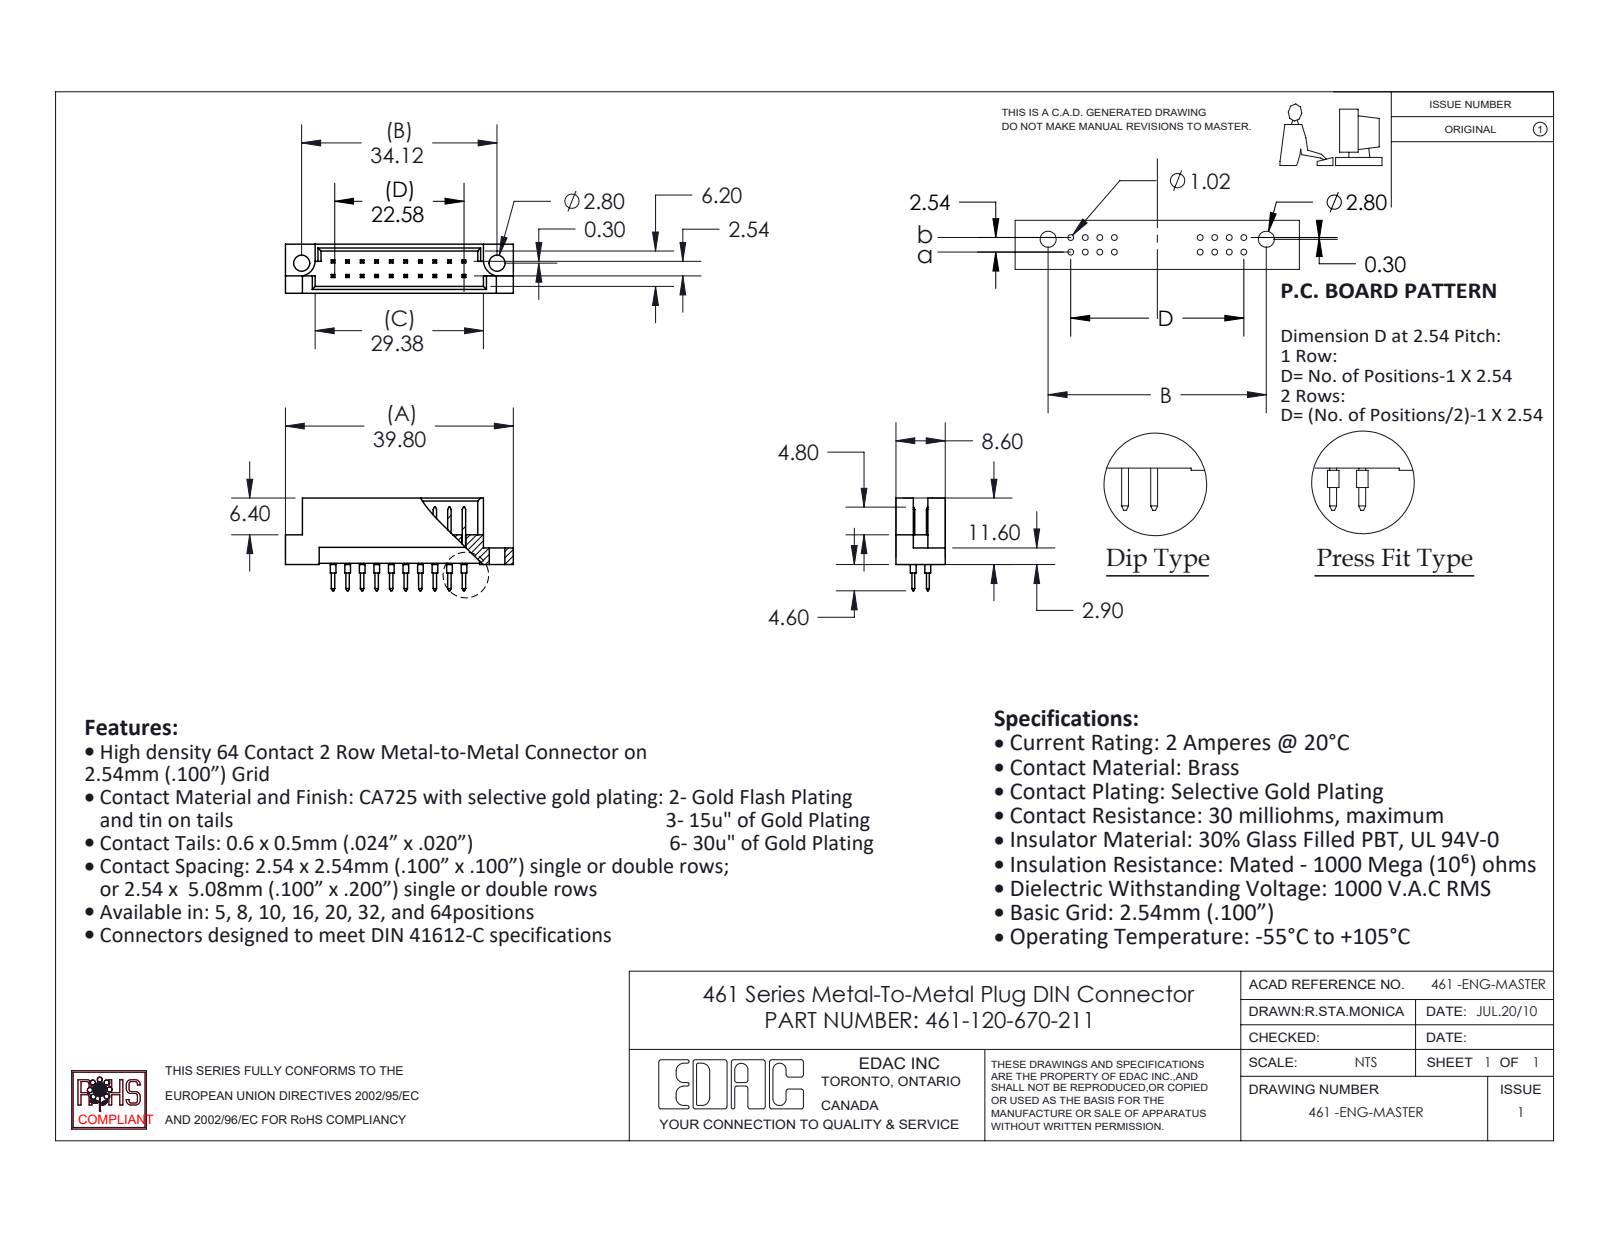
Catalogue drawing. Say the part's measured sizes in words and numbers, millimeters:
The part is named "461-120-670-211; 461 Part_20; 461-290_70". Its 3-D file was written by "SolidWorks 2020 (CONFIG_CONTROL_DESIGN)". It is 21 solids with 568 faces: 522 planar, 46 cylindrical and 0 other. Overall it measures 39.8 by 16.2 by 8.6 millimeters. Its volume is 2 005 cubic millimeters and its surface area 3 020 square millimeters. Round holes: 2 of diameter 2.8. Round bosses or shafts: 20 of diameter 1. Partial cylindrical surfaces (rounded edges, fillets, slot ends): 2 of radius 2.8. The main face-to-face distances are 1.2, 7.4, 2.54, 8.6, 6.2, 1.58, 3.28, 5.32, 2.08, 4.12. The hole center spacings are 34.12.
